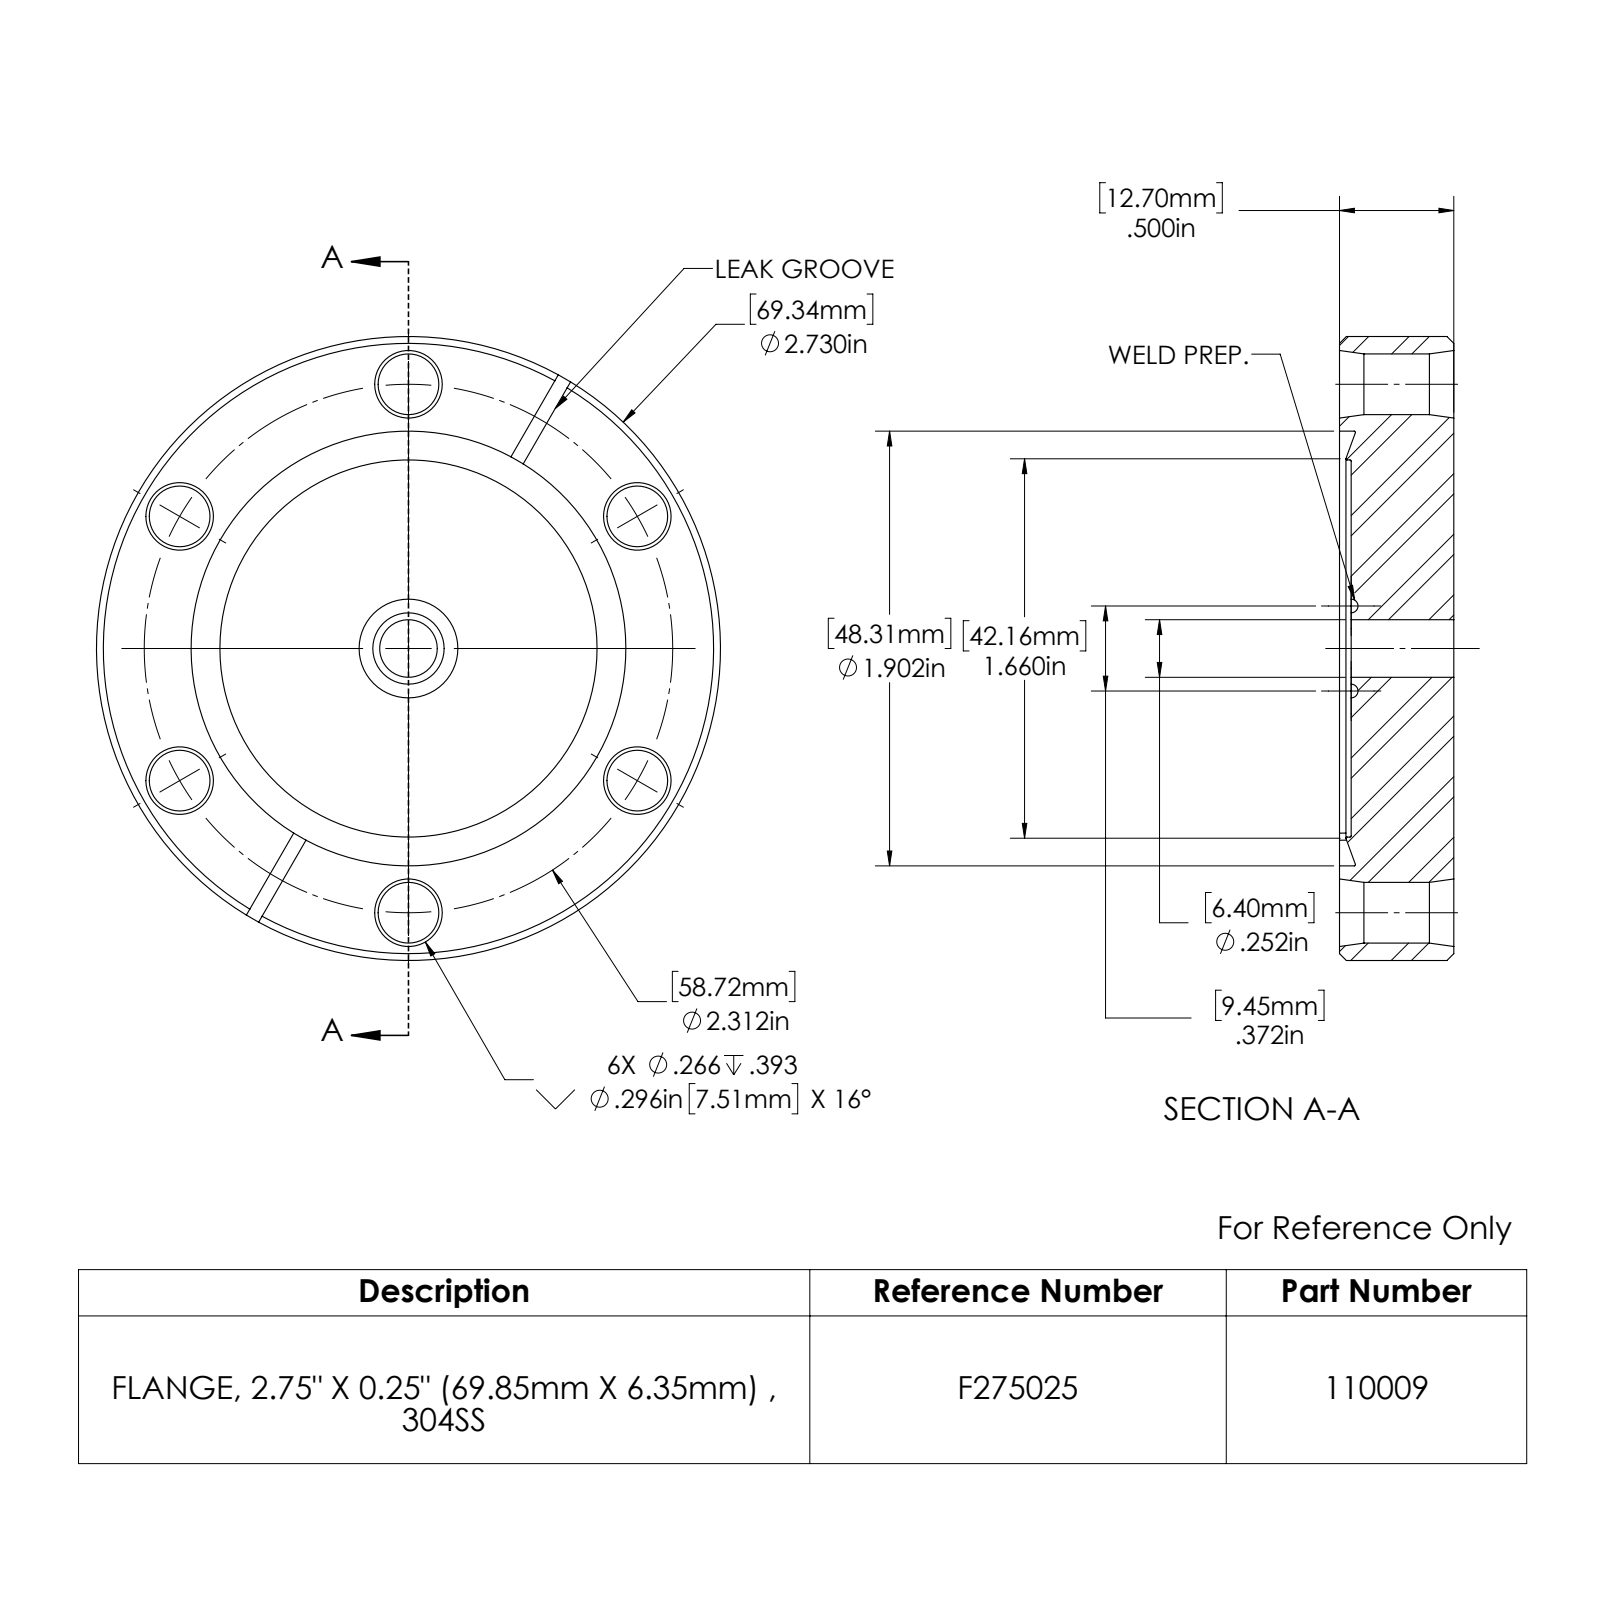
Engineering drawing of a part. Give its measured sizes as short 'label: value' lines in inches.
name: 110009_A
written by: SolidWorks 2022 (CONFIG_CONTROL_DESIGN)
unit: in
bodies: 1 solid, 70 faces (9 planar, 22 cylindrical, 39 other)
size: 2.73 × 2.73 × 0.5
volume: 2.571 in³; area: 18.44 in²
holes: 6× ⌀0.266, 1× ⌀0.252, 1× ⌀1.65, 1× ⌀1.902
bosses: 1× ⌀2.73
rounds: 2× R1.25
face distances: 0.5, 0.051, 0.449, 0.062
hole spacings: 1.156, 2.002, 2.002, 2.312, 2.312
